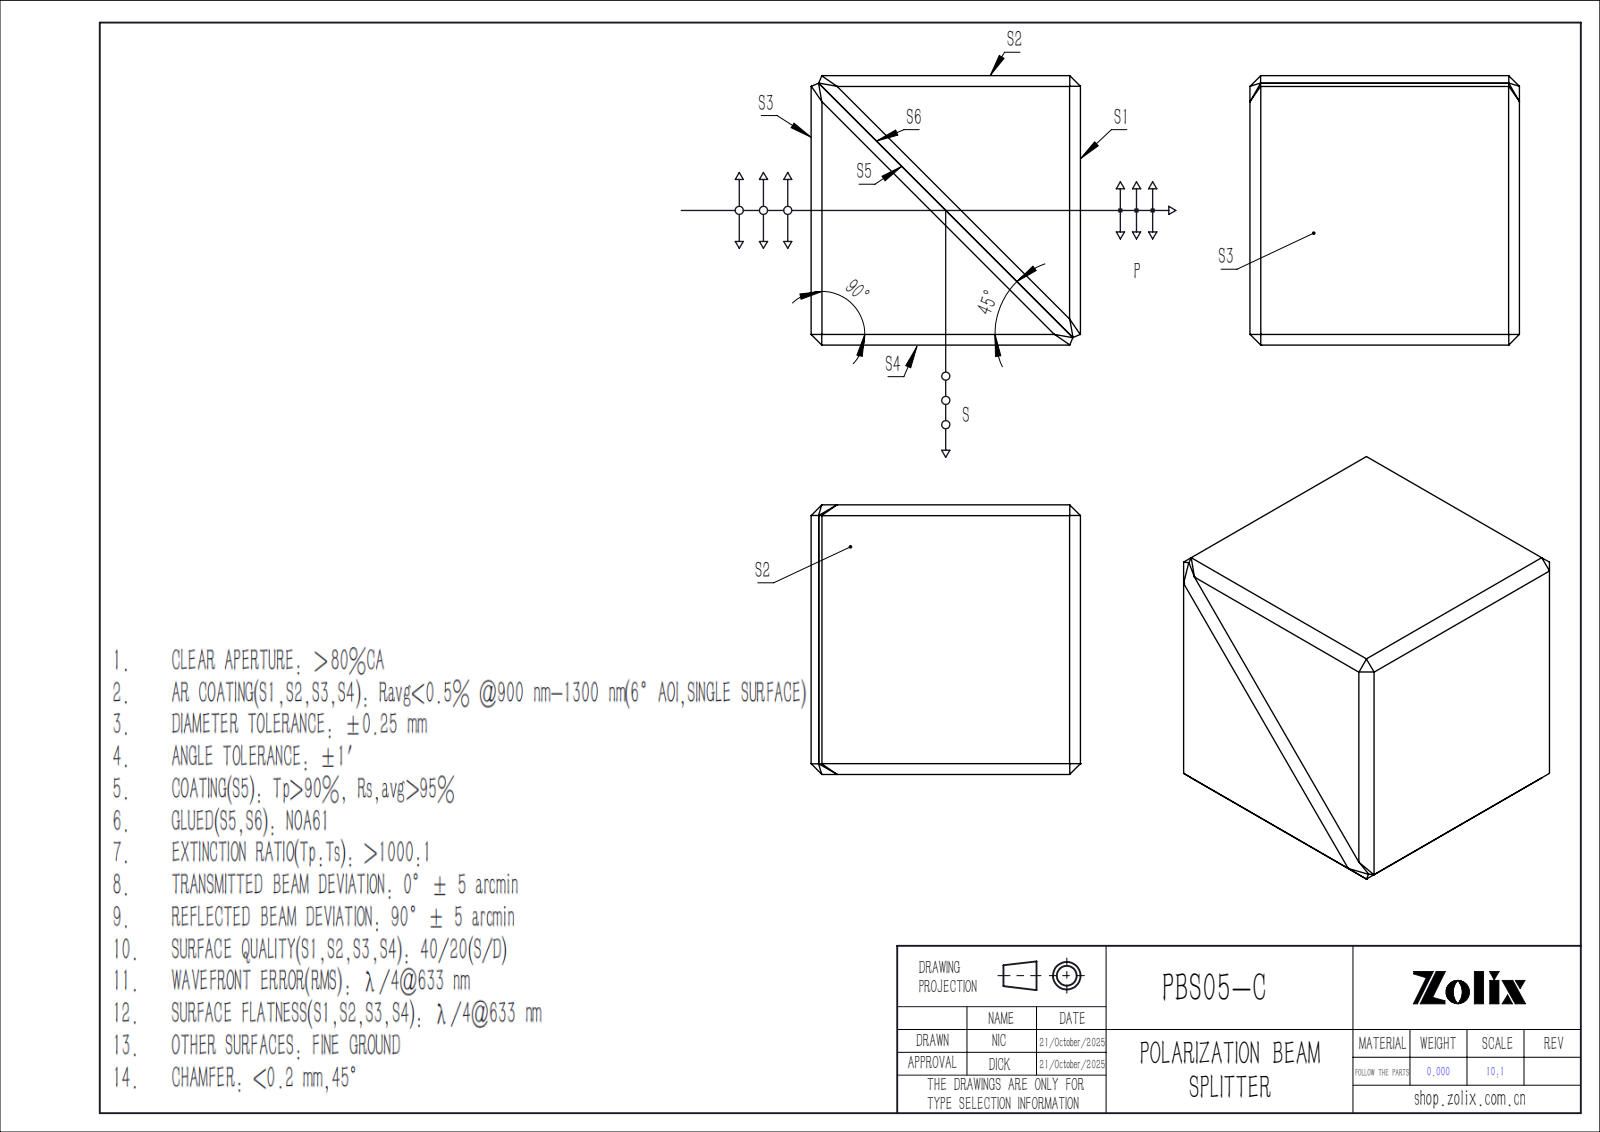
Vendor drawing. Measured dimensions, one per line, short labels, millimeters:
name: PBS603-1-2; PBS603-1-1; PBS603
written by: SolidWorks 2022 (CONFIG_CONTROL_DESIGN)
unit: mm
bodies: 2 solids, 43 faces (41 planar, 2 cylindrical, 0 other)
size: 5 × 5 × 5
volume: 123 mm³; area: 206 mm²
holes: 1× ⌀0.2
face distances: 5, 6.79, 3.25, 3.39, 6.78, 6.16, 6.17, 7.08, 8.2, 8.19
